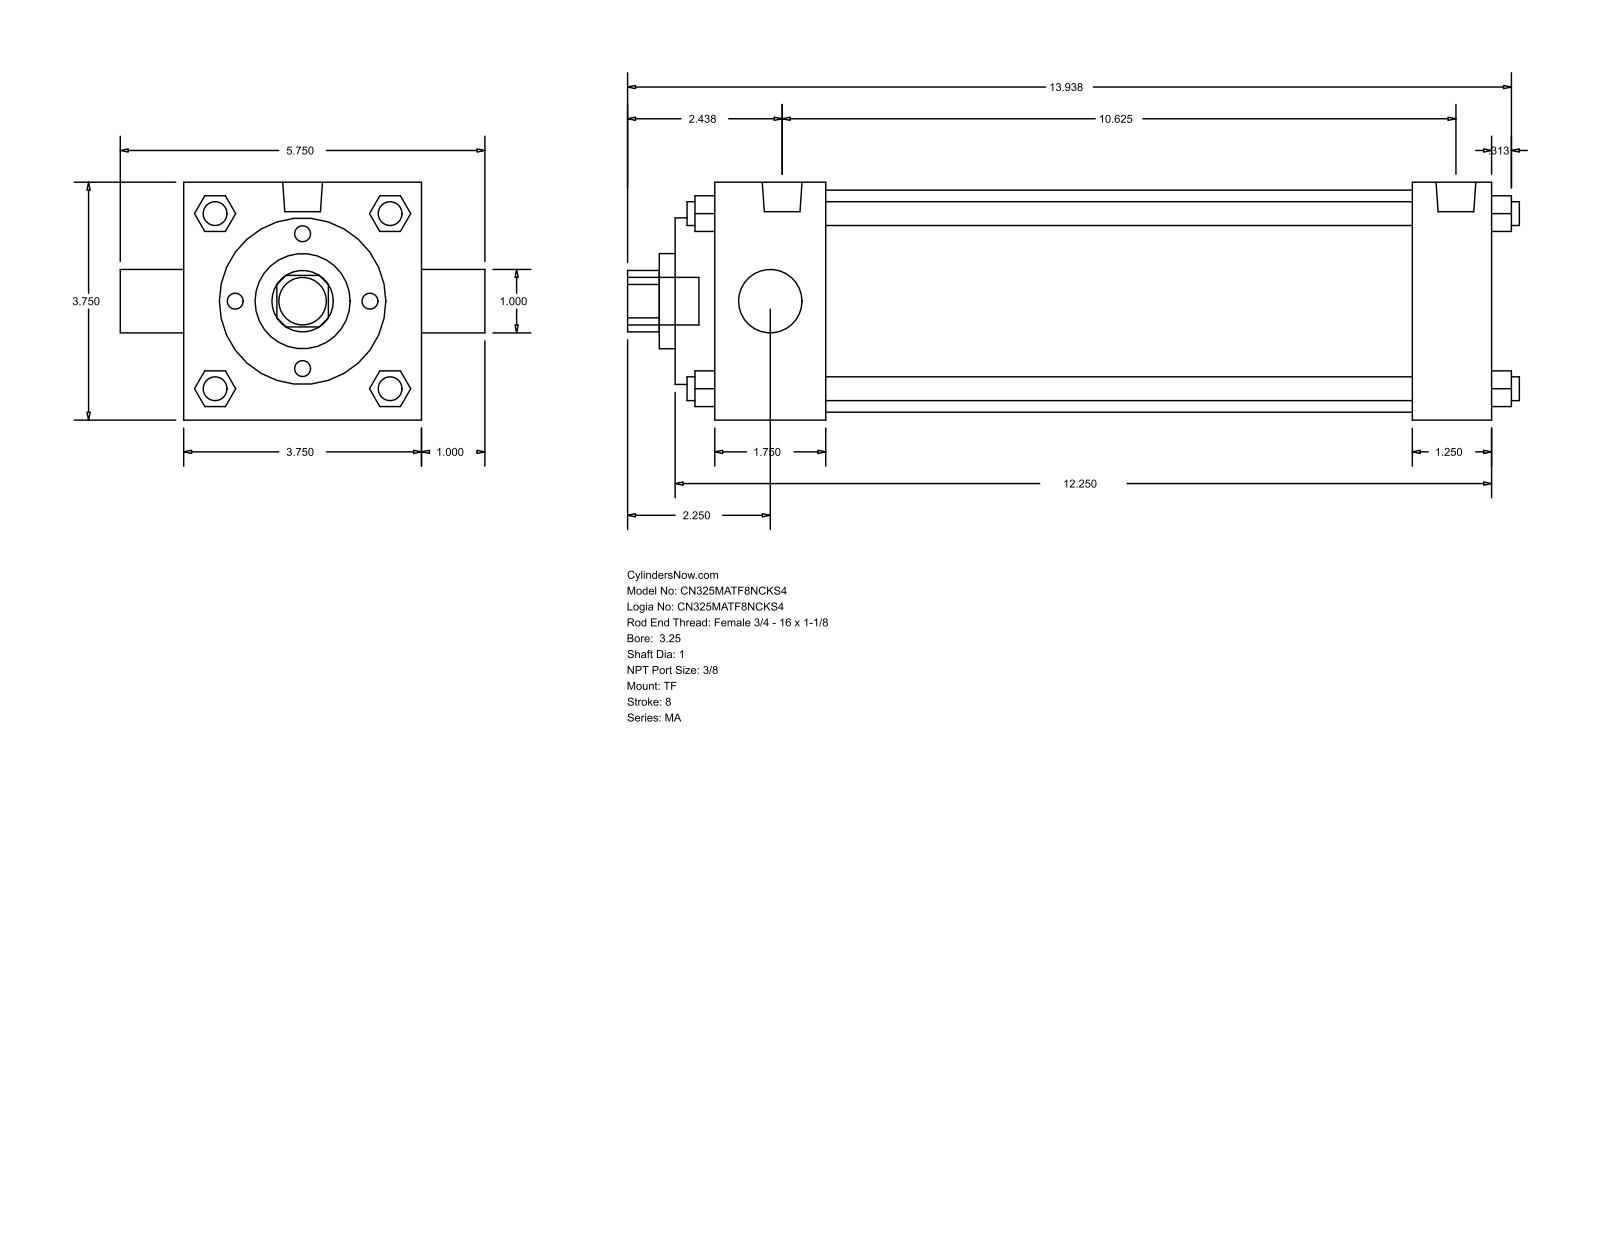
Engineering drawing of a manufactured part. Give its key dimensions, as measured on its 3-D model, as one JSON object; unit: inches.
{"part_name": "MA_TF__0325_1", "step_written_by": "GSSL Pune (CONFIG_CONTROL_DESIGN)", "units": "inches", "bodies": {"solids": 0, "faces": 122, "planar": 93, "cylindrical": 29, "other": 0}, "overall_size": [14.063, 5.75, 3.75], "round_holes": [[1, 2], [1.5, 1], [2.625, 1], [3.5, 1]], "round_bosses_or_shafts": [[0.375, 4], [0.437, 3], [0.627, 2], [0.75, 1]], "partial_cylinders_radius": [[0.484, 1]], "face_to_face_distances": [3.75, 12.25, 12.875, 0.625, 1.75, 11, 9.25, 10.5, 1.25, 2.375]}
